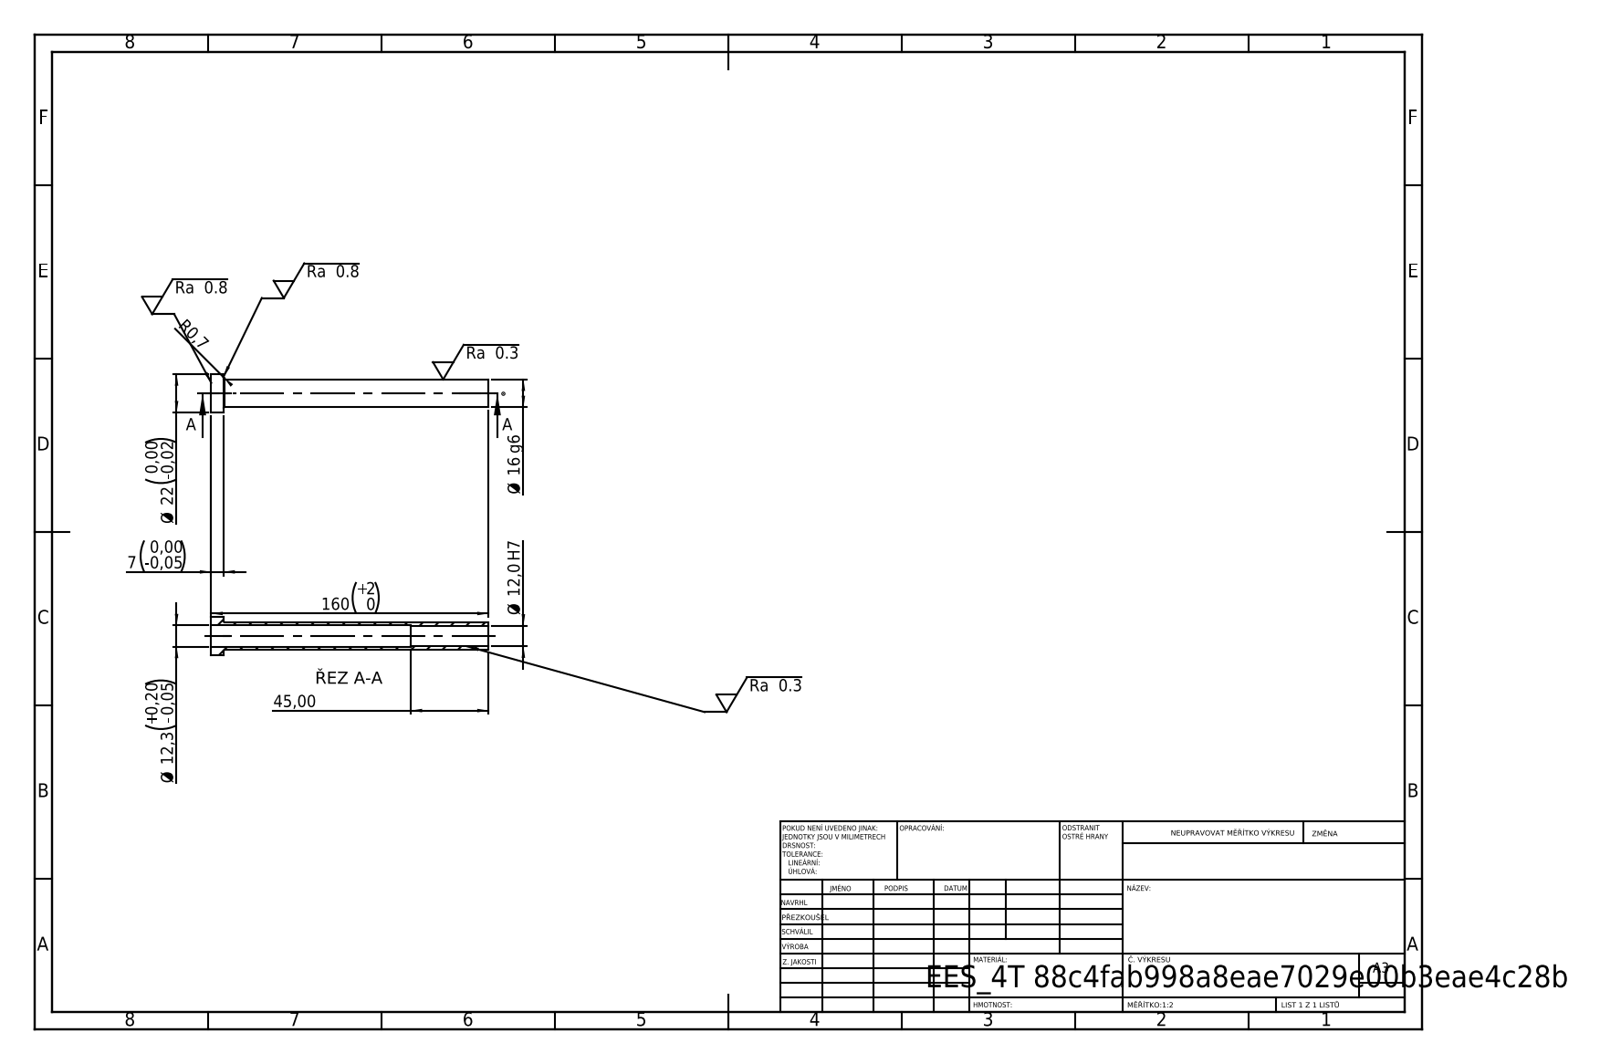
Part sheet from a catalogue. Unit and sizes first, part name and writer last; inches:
Units: inches
Overall size (bounding box): 6.299 × 0.866 × 0.866
Round holes (diameter × count): ⌀0.472 ×1, ⌀0.484 ×1
Round bosses / shafts (diameter × count): ⌀0.866 ×1, ⌀0.63 ×1
Main face-to-face distances: 0.276, 6.299, 6.024, 4.528, 4.252, 1.772
Volume: 0.896 in³ · Surface area: 22.99 in²
Bodies: 1 solid, 14 faces (4 planar, 8 cylindrical, 2 other)
STEP written by: SolidWorks 2019 (CONFIG_CONTROL_DESIGN)
